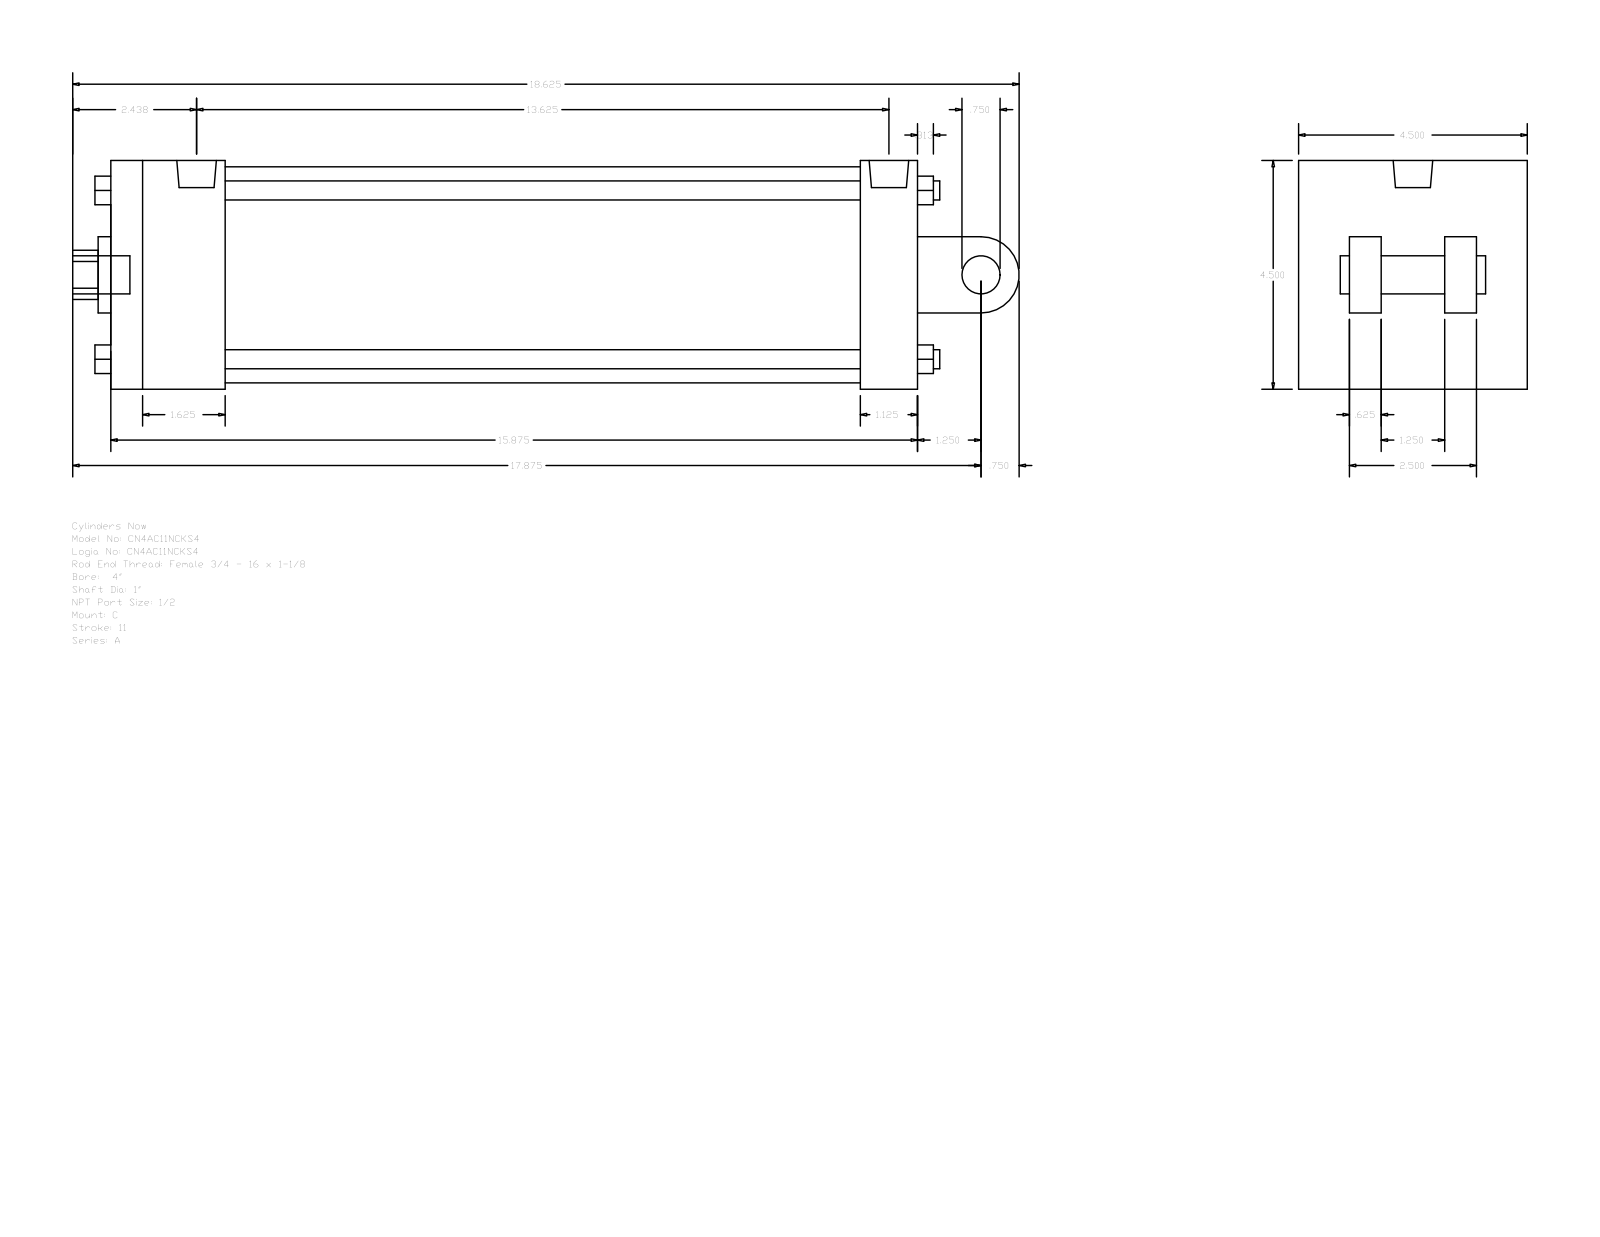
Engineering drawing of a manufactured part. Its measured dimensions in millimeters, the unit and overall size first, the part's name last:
Units: millimetres
Overall size (bounding box): 473.07 × 114.3 × 114.3
Round holes (diameter × count): ⌀8.73 ×2, ⌀19.77 ×1, ⌀25.4 ×1, ⌀38.1 ×1, ⌀107.95 ×1
Round bosses / shafts (diameter × count): ⌀9.53 ×4, ⌀19.05 ×2, ⌀8.73 ×2, ⌀19.77 ×1
Partial cylindrical surfaces — rounded edges, fillets, slot ends (radius × count): R12.29 ×1, R19.05 ×1
Main face-to-face distances: 114.3, 403.22, 73.03, 28.57, 374.65, 57.15, 317.5, 346.07, 15.87, 47.63
Hole centre spacings: 3.18
Bodies: 0 solids, 135 faces (102 planar, 33 cylindrical, 0 other)
Part name (STEP PRODUCT): A_C__0400_1
STEP written by: GSSL Pune (CONFIG_CONTROL_DESIGN)
